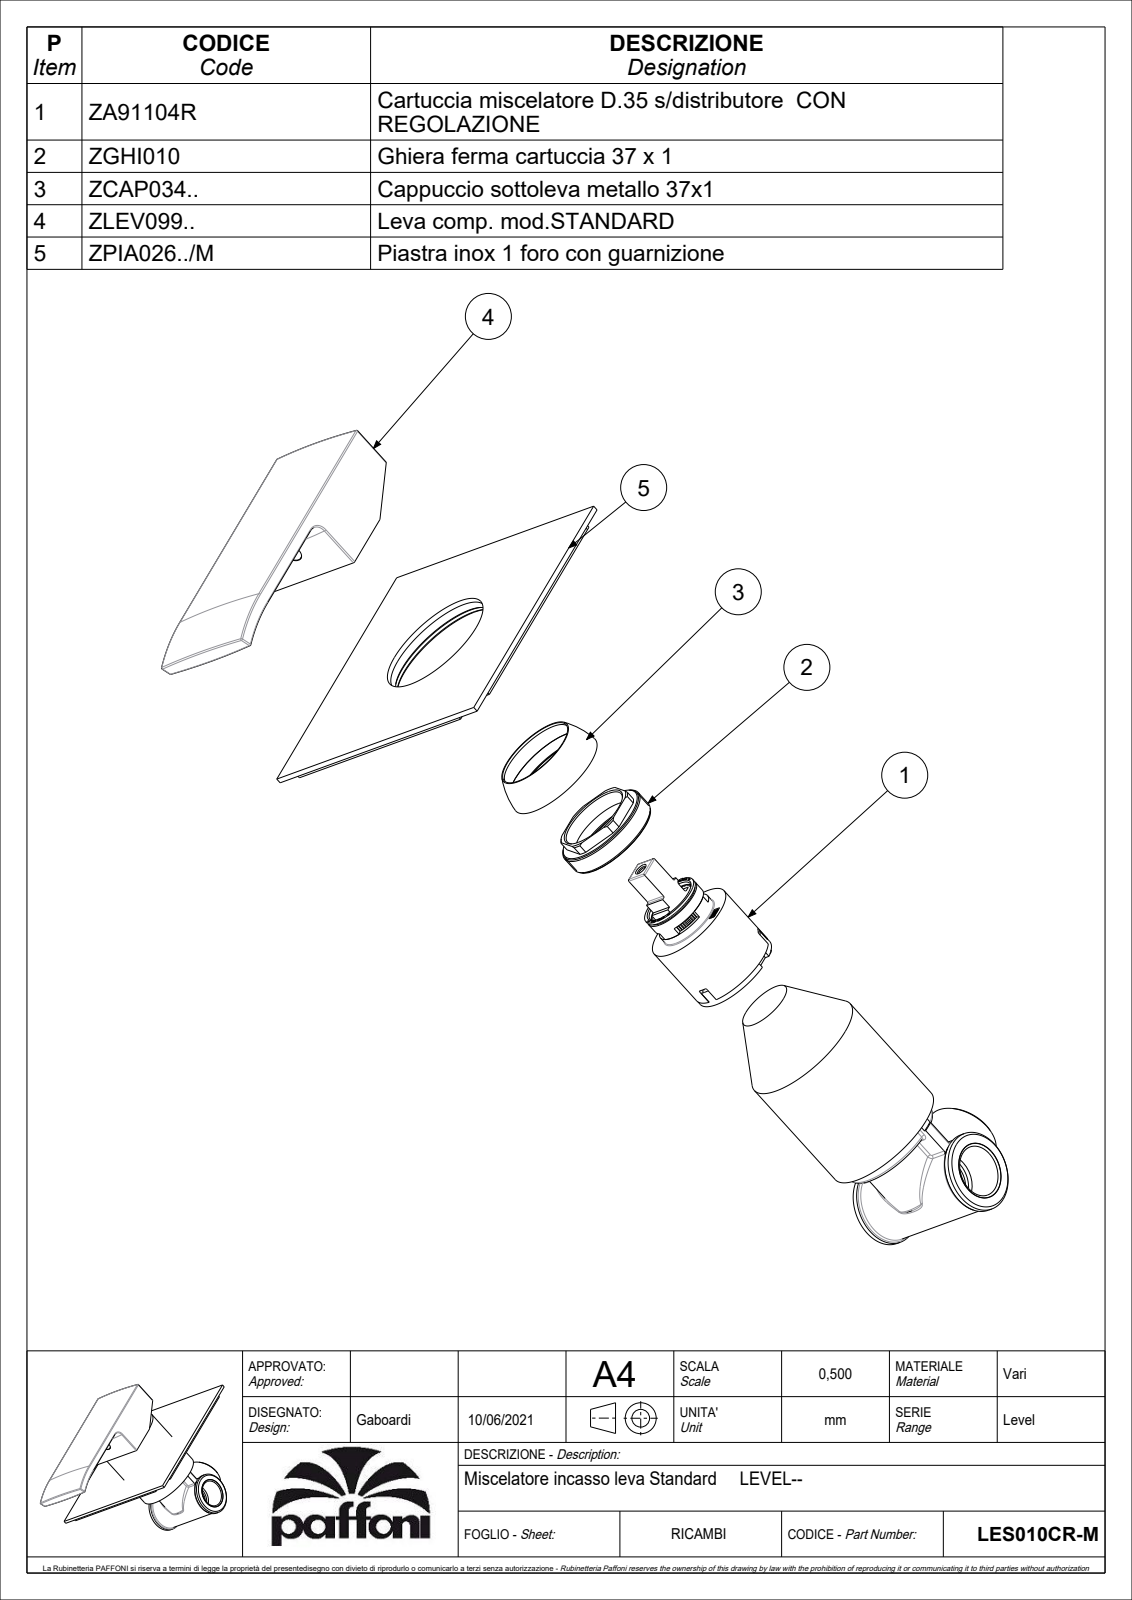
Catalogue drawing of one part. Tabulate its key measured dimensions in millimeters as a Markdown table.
| quantity | value |
| --- | --- |
| part name | LES010CR-M |
| STEP written by | CREO PARAMETRIC BY PTC INC, 2020044 (CONFIG_CONTROL_DESIGN) |
| units | millimeters |
| bodies | 2 solids, 859 faces (540 planar, 190 cylindrical, 129 other) |
| overall size | 143.38 × 110 × 52.1 |
| volume | 78 958 mm³ |
| surface area | 60 008 mm² |
| round holes (diameter × count) | 4 × 2, 3 × 1, 3.3 × 1, 5 × 1, 5.5 × 1, 7.8 × 1, 19.5 × 1, 19.9 × 1, 26.8 × 1, 29 × 1, 31 × 1, 32.4 × 1 |
| round bosses / shafts (diameter × count) | 44.8 × 1, 35 × 1, 23.5 × 1, 23.4 × 1, 21.8 × 1, 7.6 × 1 |
| partial cylindrical surfaces (radius × count) | 1.5 × 14, 0.5 × 12, 0.15 × 11, 0.3 × 4, 2 × 4, 1 × 2, 300 × 2, 2.25 × 1 |
| main face-to-face distances | 2, 45, 49.3, 47.3, 32.5, 77.5, 13.5, 15, 15.5, 5.5 |
| hole center spacings | 8 |
